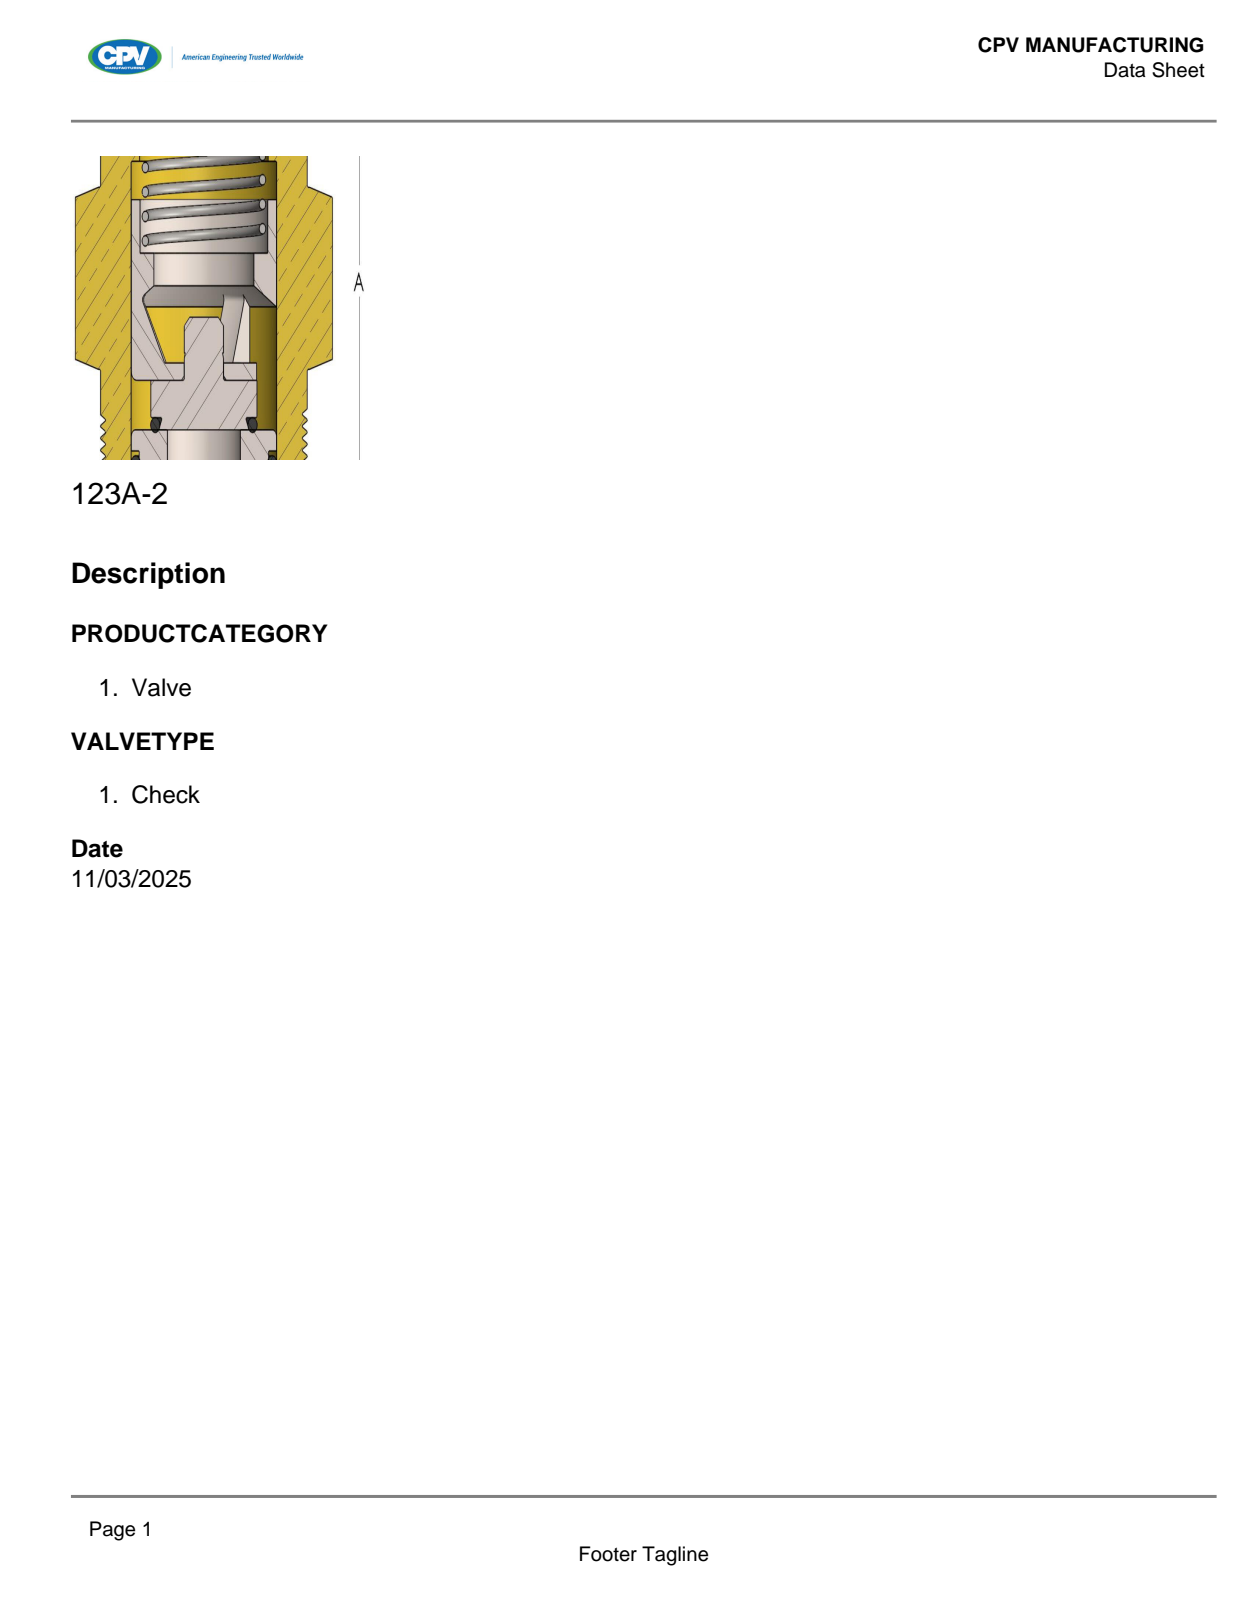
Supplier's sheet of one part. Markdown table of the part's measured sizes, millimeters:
| quantity | value |
| --- | --- |
| part name | 123A-2 |
| STEP written by | SolidWorks 2018 (AUTOMOTIVE_DESIGN) |
| units | millimeters |
| bodies | 1 solid, 73 faces (15 planar, 30 cylindrical, 28 other) |
| overall size | 48.1 × 44 × 38.1 |
| volume | 46 330 mm³ |
| surface area | 9 858 mm² |
| round holes (diameter × count) | 11.2 × 1, 11.2 × 1 |
| round bosses / shafts (diameter × count) | 34.8 × 1, 28.3 × 1 |
| main face-to-face distances | 38.1, 48.1, 12.7, 30.6, 17.5, 17.9, 30.2, 0.4, 17.5, 30.2 |
